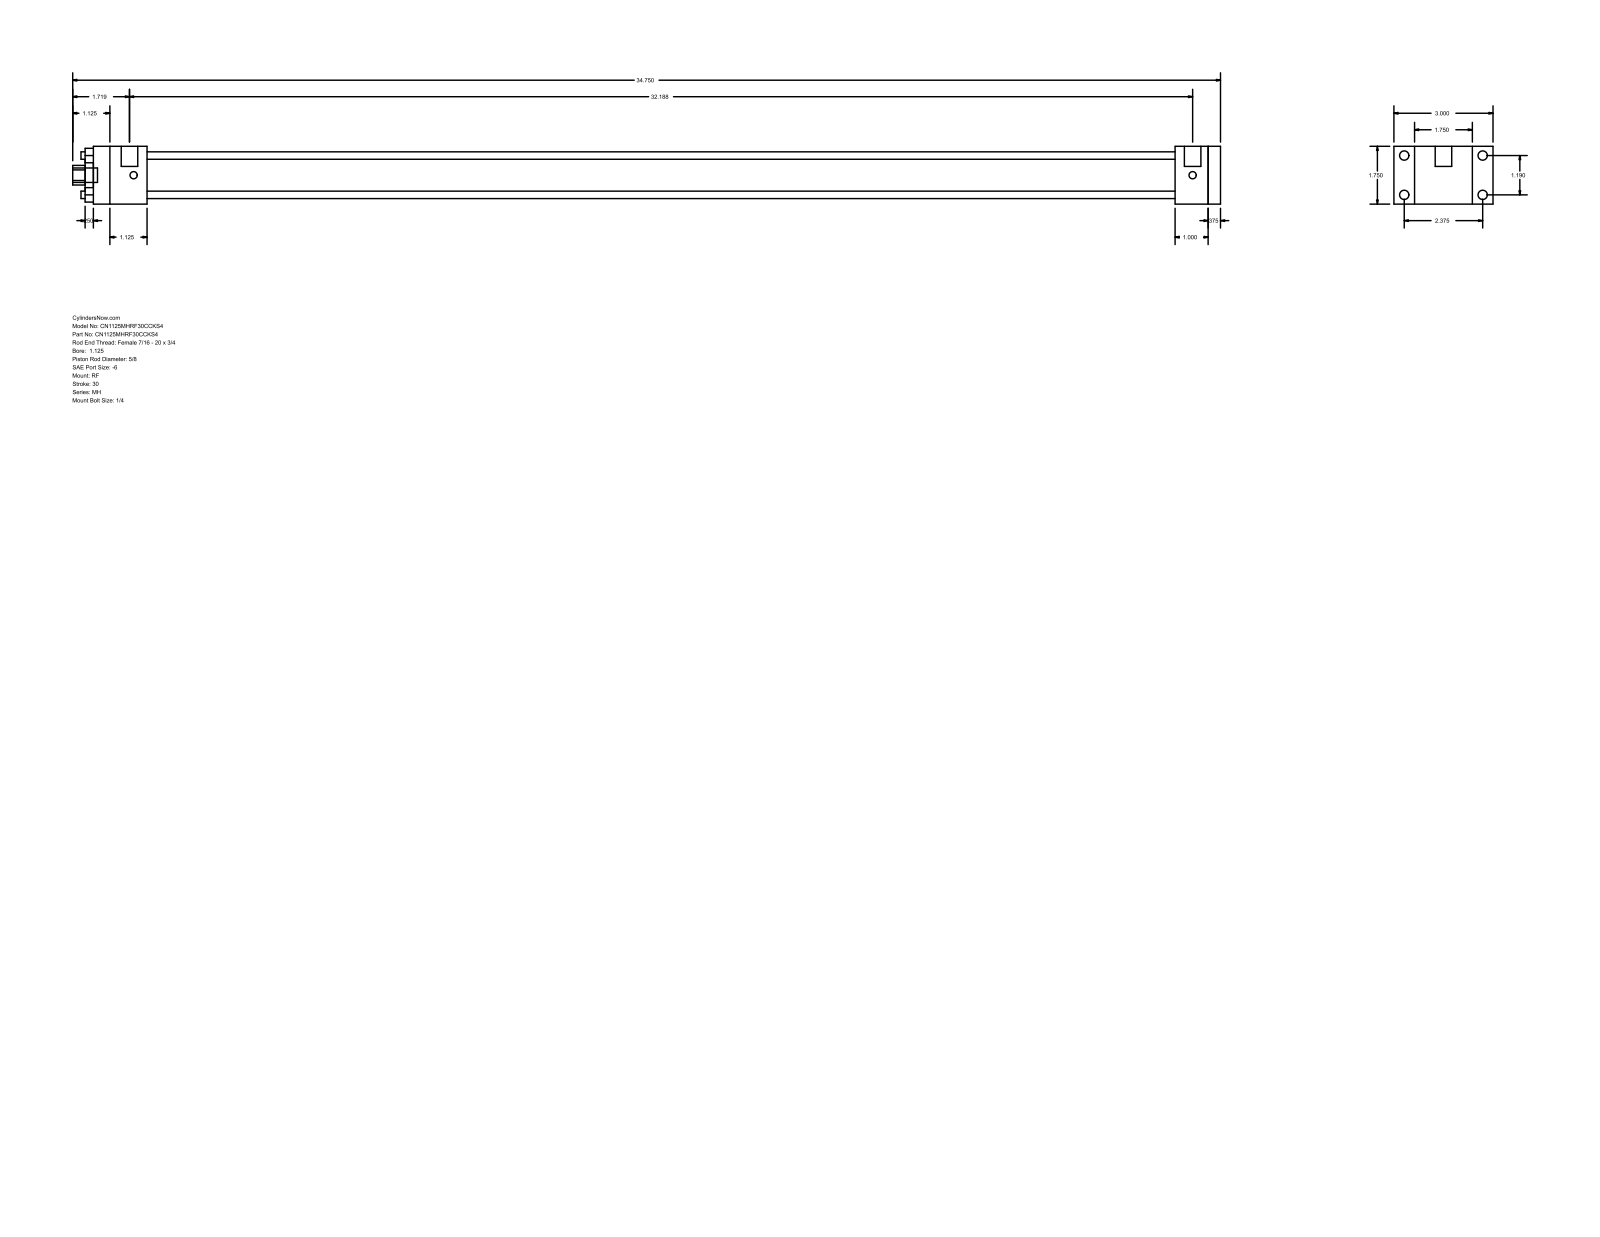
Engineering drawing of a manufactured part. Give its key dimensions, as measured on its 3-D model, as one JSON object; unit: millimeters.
{"part_name": "MH_RF__0112_0.625", "step_written_by": "GSSL Pune (CONFIG_CONTROL_DESIGN)", "units": "millimeters", "bodies": {"solids": 0, "faces": 92, "planar": 64, "cylindrical": 28, "other": 0}, "overall_size": [882.65, 76.2, 44.45], "round_holes": [[5.71, 4], [15.88, 1], [28.57, 1], [34.92, 1]], "round_bosses_or_shafts": [[7.14, 4], [5.56, 4], [12.7, 2], [11.11, 1]], "partial_cylinders_radius": [[7.54, 1]], "face_to_face_distances": [44.46, 9.53, 866.77, 15.87, 815.97, 825.5, 790.58, 25.39, 34.92, 41.27], "hole_center_spacings": [21.37, 30.22, 42.74]}
